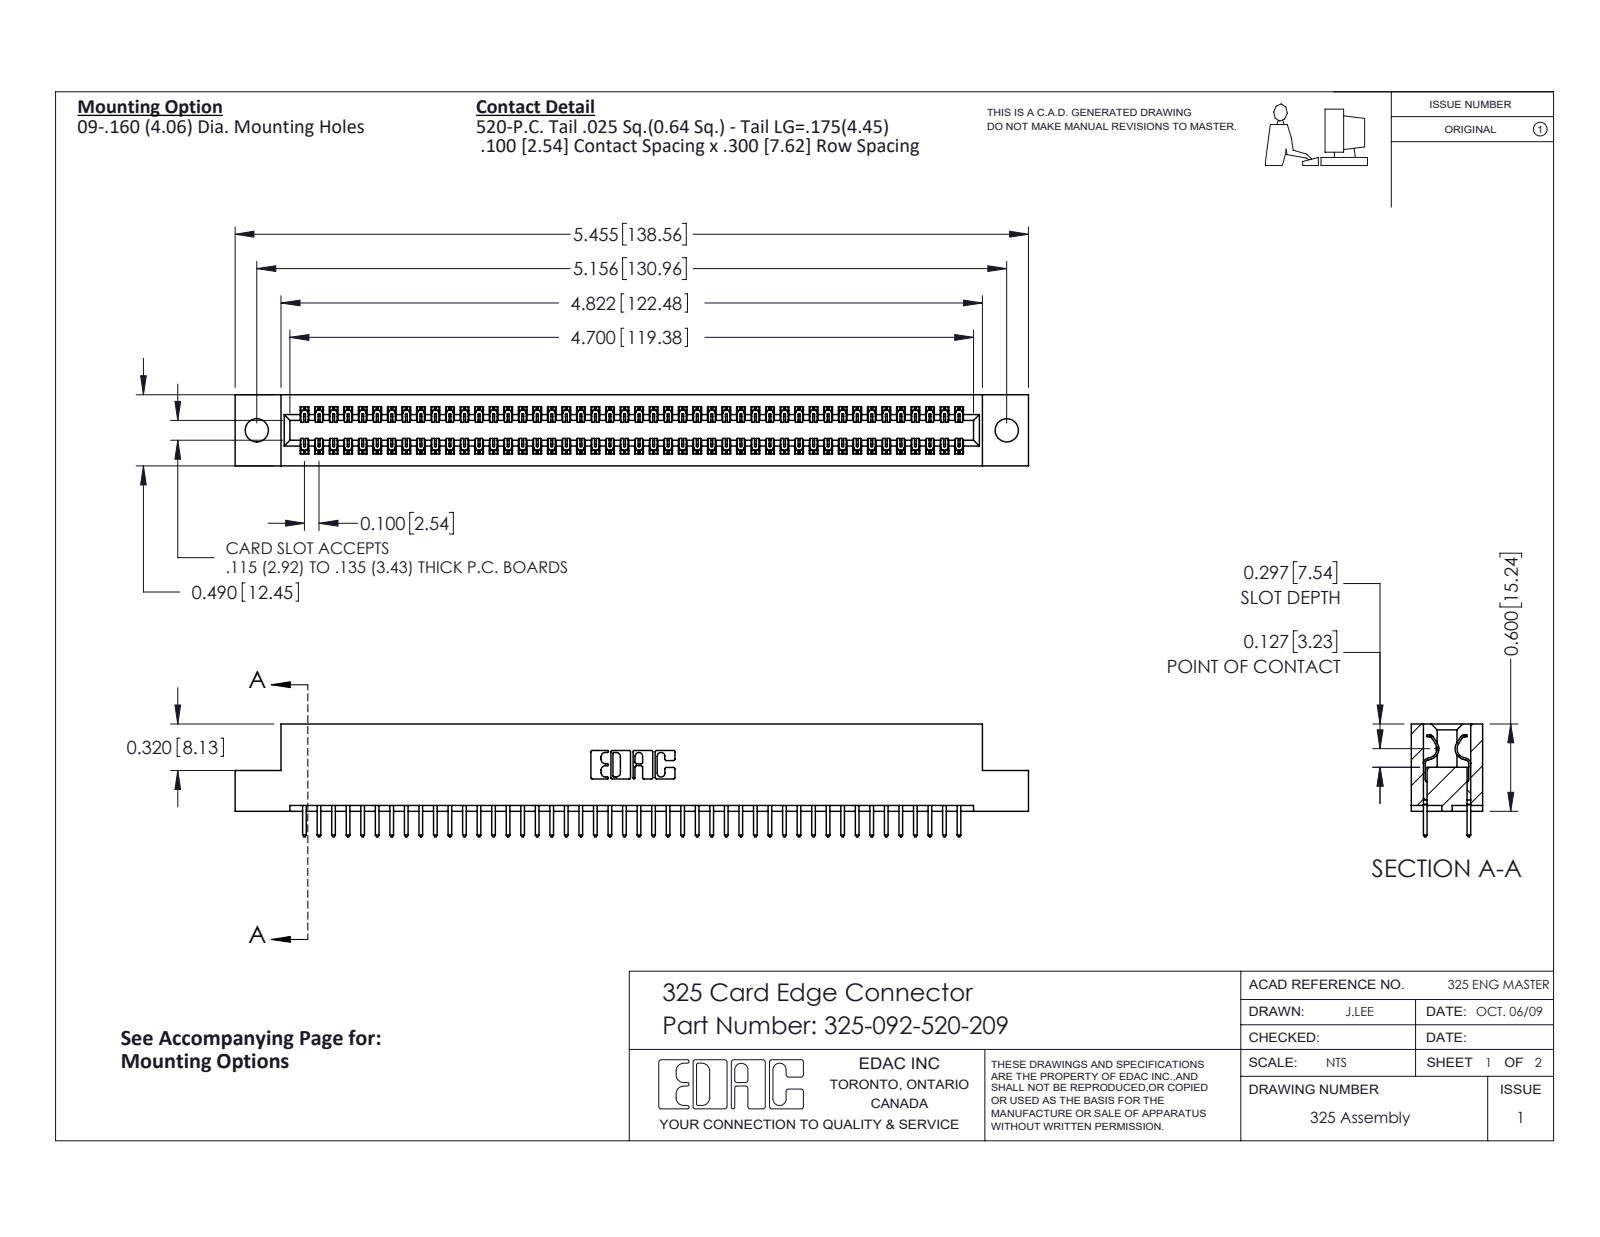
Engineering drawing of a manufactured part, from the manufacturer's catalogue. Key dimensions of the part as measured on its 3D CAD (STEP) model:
Part name (STEP PRODUCT): 325-092-520-209; 325-292-001_325-293-120; 325 Part_.160 TH
STEP written by: SolidWorks 2016 (CONFIG_CONTROL_DESIGN)
Units: inches
Bodies: 93 solids, 4898 faces (3382 planar, 1516 cylindrical, 0 other)
Overall size (bounding box): 5.455 × 0.775 × 0.49
Volume: 1.079 in³ · Surface area: 32.9 in²
Round holes (diameter × count): ⌀0.16 ×2
Partial cylindrical surfaces — rounded edges, fillets, slot ends (radius × count): R0.006 ×138, R0.01 ×92, R0.01 ×22, R0.007 ×6, R0.031 ×6, R0.026 ×3, R0.014 ×2, R0.022 ×2
Main face-to-face distances: 0.083, 0.407, 0.3, 0.49, 0.107, 0.383, 0.025, 0.325, 0.275, 0.56
Hole centre spacings: 5.156
